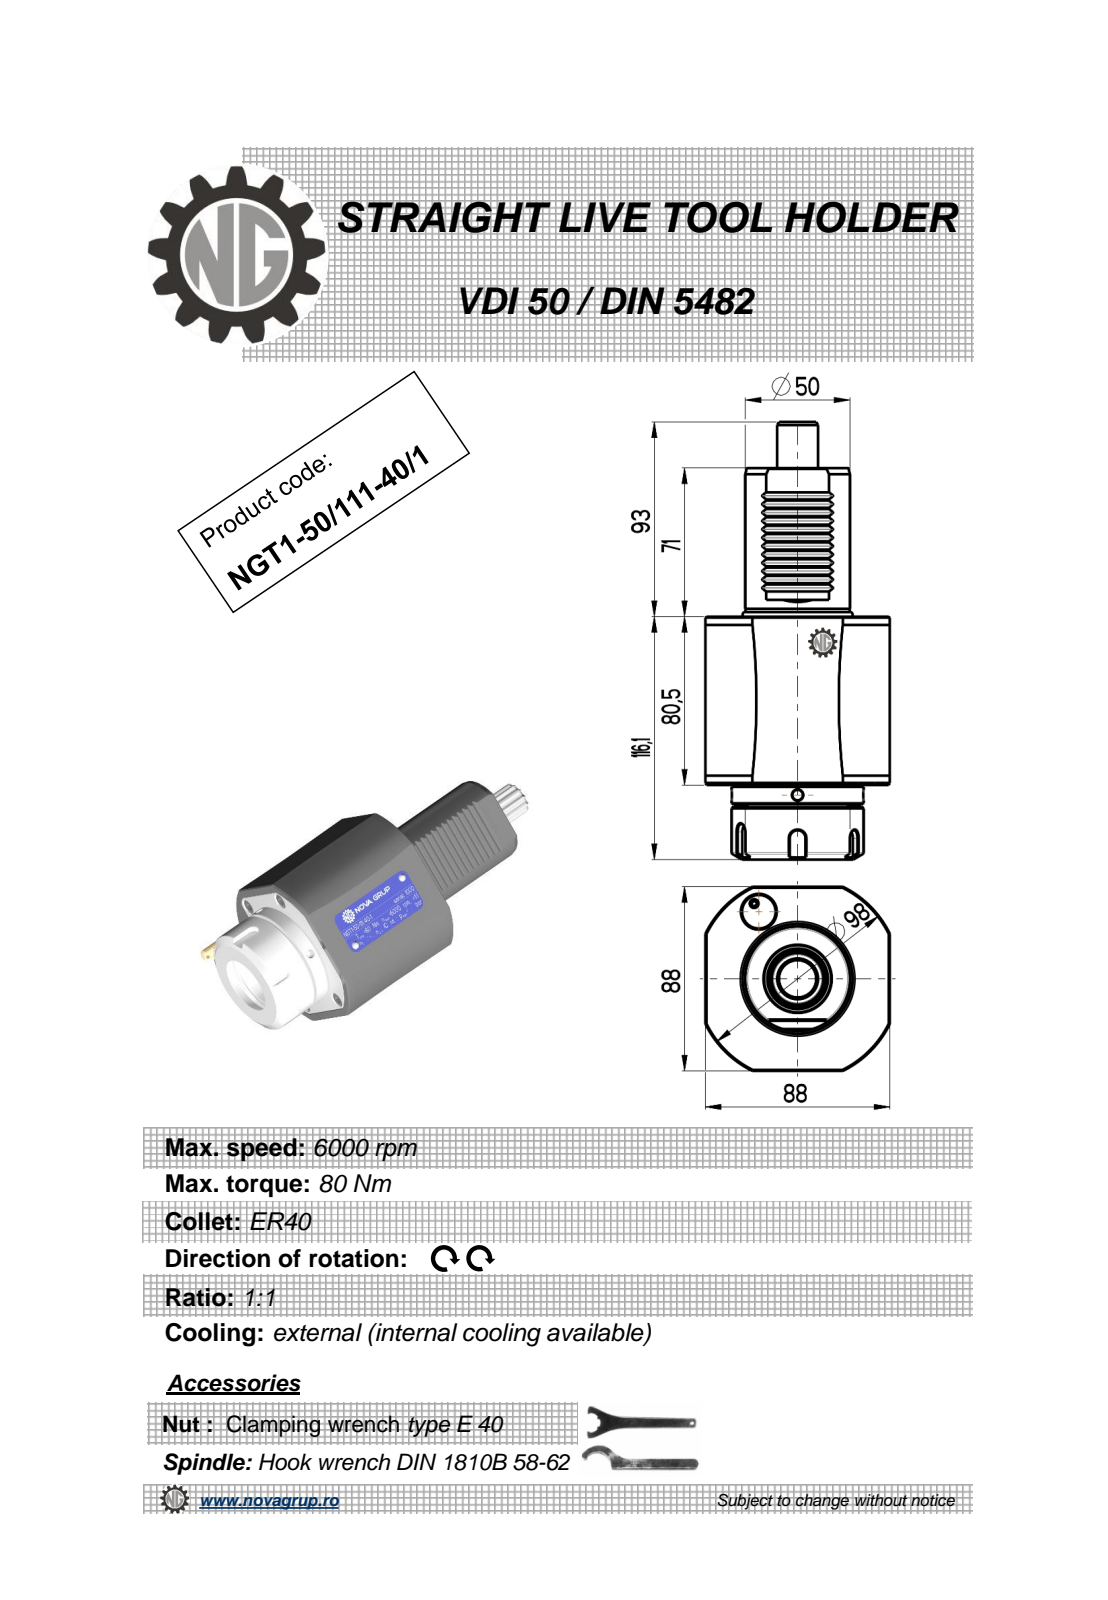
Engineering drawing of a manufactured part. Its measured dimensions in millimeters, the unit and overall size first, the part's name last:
Units: millimetres
Overall size (bounding box): 209.1 × 89.6 × 88
Round holes (diameter × count): ⌀5 ×2, ⌀2.5 ×1, ⌀3 ×1
Round bosses / shafts (diameter × count): ⌀63 ×1, ⌀51 ×1, ⌀50 ×1, ⌀9 ×1, ⌀7 ×1, ⌀5 ×1
Partial cylindrical surfaces — rounded edges, fillets, slot ends (radius × count): R3.33 ×24, R0.3 ×12, R2.5 ×12, R3.75 ×5, R8.2 ×1, R9.75 ×1, R49 ×1
Main face-to-face distances: 88, 80.5, 71, 151.5, 187.1, 116.1, 35.6, 180.9, 109.9, 29.4
Volume: 792 534 mm³ · Surface area: 64 961 mm²
Bodies: 1 solid, 315 faces (100 planar, 117 cylindrical, 98 other)
Part name (STEP PRODUCT): NGT1_50_111_40_1
STEP written by: PRO/ENGINEER BY PARAMETRIC TECHNOLOGY CORPORATION, 2010280 (CONFIG_CONTROL_DESIGN)
